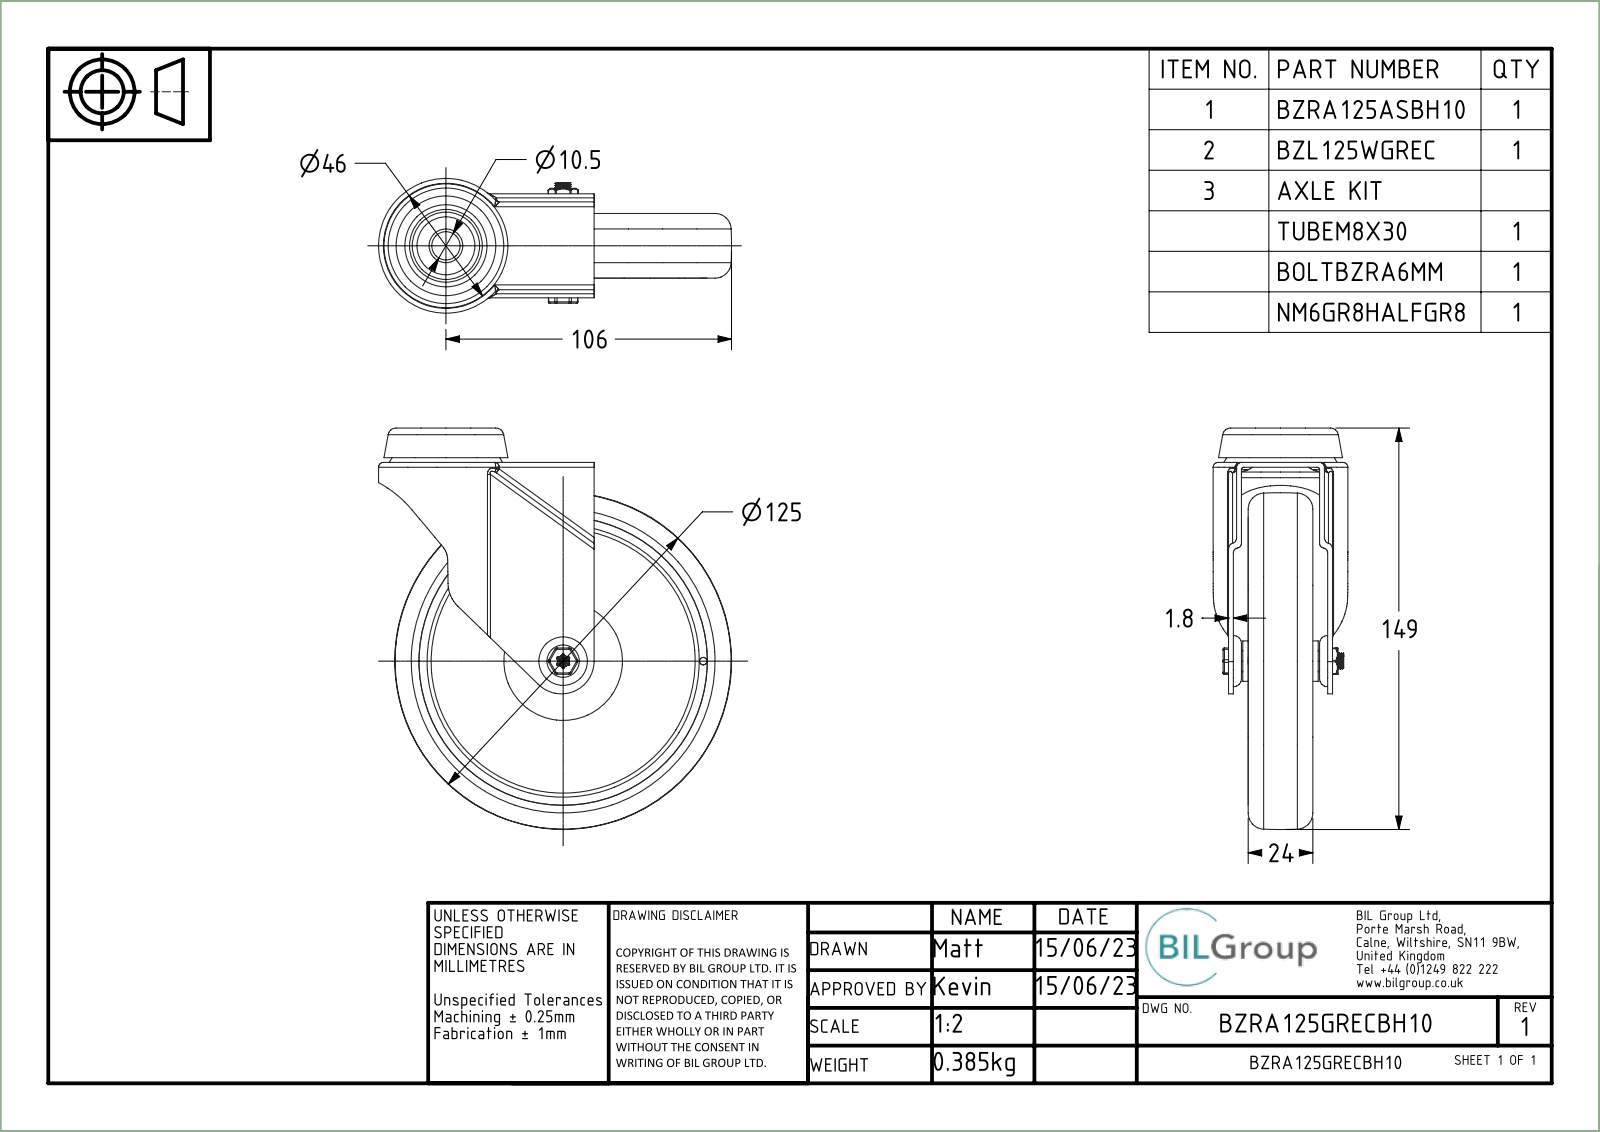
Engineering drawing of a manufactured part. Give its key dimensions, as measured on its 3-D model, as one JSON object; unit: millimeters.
{"part_name": "BZRA125ASBH10; ZINC PLATED PRESSED STEEL FORKS; ZINC PLATED PRESSED STEEL HEAD; BZRA125GRECBH10 (+8 more)", "step_written_by": "Spatial InterOp 3D (CONFIG_CONTROL_DESIGN)", "units": "millimeters", "bodies": {"solids": 8, "faces": 404, "planar": 64, "cylindrical": 181, "other": 159}, "overall_size": [149, 131, 50], "volume_mm3": 169527, "surface_area_mm2": 91993, "round_holes": [[2.75, 1], [6, 1], [6.3, 1], [6.4, 1], [8.1, 1], [8.3, 1], [10.5, 1], [10.56, 1], [28, 1], [101, 1], [107, 1]], "round_bosses_or_shafts": [[39, 1], [18, 1], [15, 1], [14.76, 1], [8, 1], [7.95, 1], [5, 1]], "partial_cylinders_radius": [[1, 18], [1.8, 14], [0.5, 12], [0.4, 6], [0.9, 6], [2.12, 1], [8, 1], [12, 1]], "face_to_face_distances": [4, 1.8, 17.3, 21.3, 10, 7.3, 31.3, 14, 3, 33.8], "hole_center_spacings": [52]}
